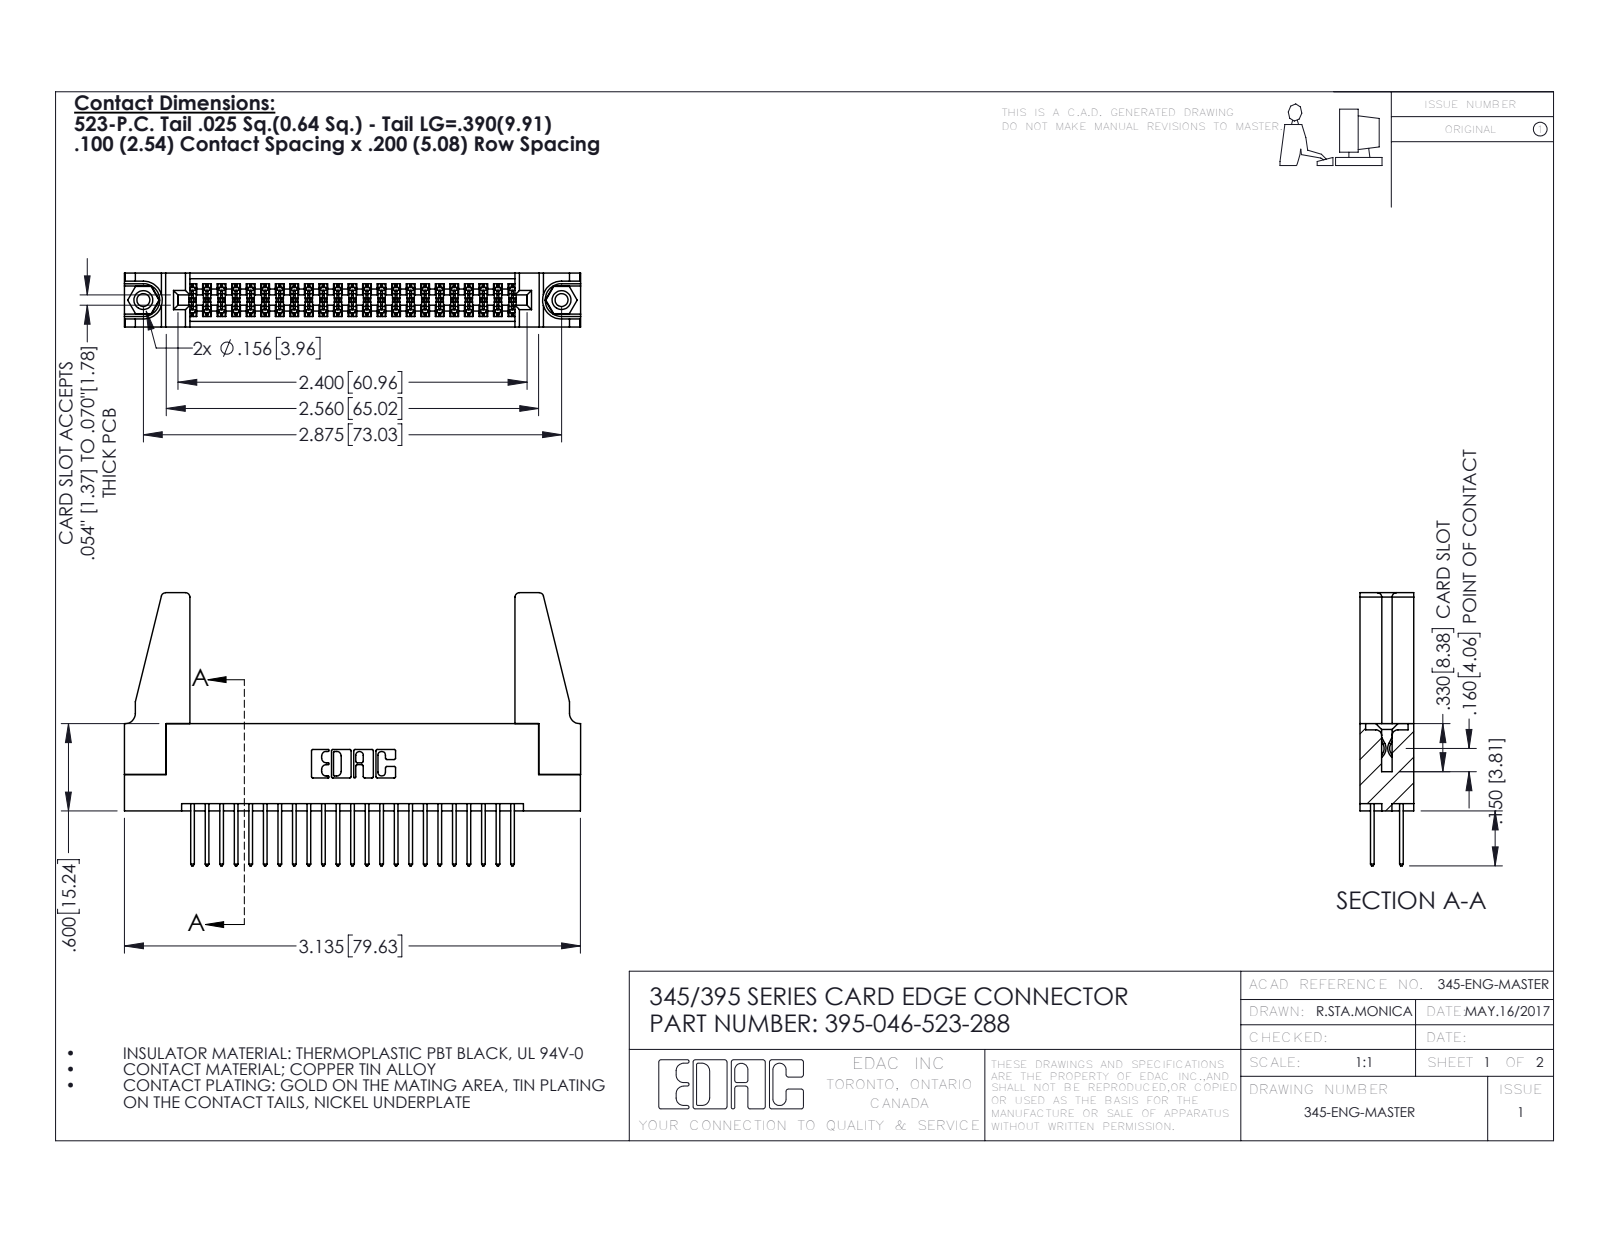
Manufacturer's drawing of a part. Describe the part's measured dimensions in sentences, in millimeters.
The part is named "395-046-523-288; 345-220-078_345-220-088; 345 Part_Flush Mounting Lugs - 0.156 Dia-TH; 345-292-001_345-293-123 (+1 more)". Its 3-D file was written by "SolidWorks 2016 (CONFIG_CONTROL_DESIGN)". It is 51 solids with 2550 faces: 1670 planar, 864 cylindrical and 16 other. Overall it measures 79.7 by 47.7 by 9.4 millimeters. Its volume is 10 900 cubic millimeters and its surface area 14 490 square millimeters. Round holes: 2 of diameter 2.3, 2 of diameter 3.2, 2 of diameter 4, 1 of diameter 1.6. Round bosses or shafts: 2 of diameter 3.9. Partial cylindrical surfaces (rounded edges, fillets, slot ends): 69 of radius 0.2, 46 of radius 0.3, 22 of radius 0.3, 8 of radius 0.8, 6 of radius 0.2, 6 of radius 0.8, 3 of radius 0.7, 2 of radius 0.4. The main face-to-face distances are 1.8, 7.6, 9.4, 5.1, 2.5, 6.9, 0.6, 5.7, 4.4, 3.8. The hole center spacings are 6.9, 67.1, 73.
